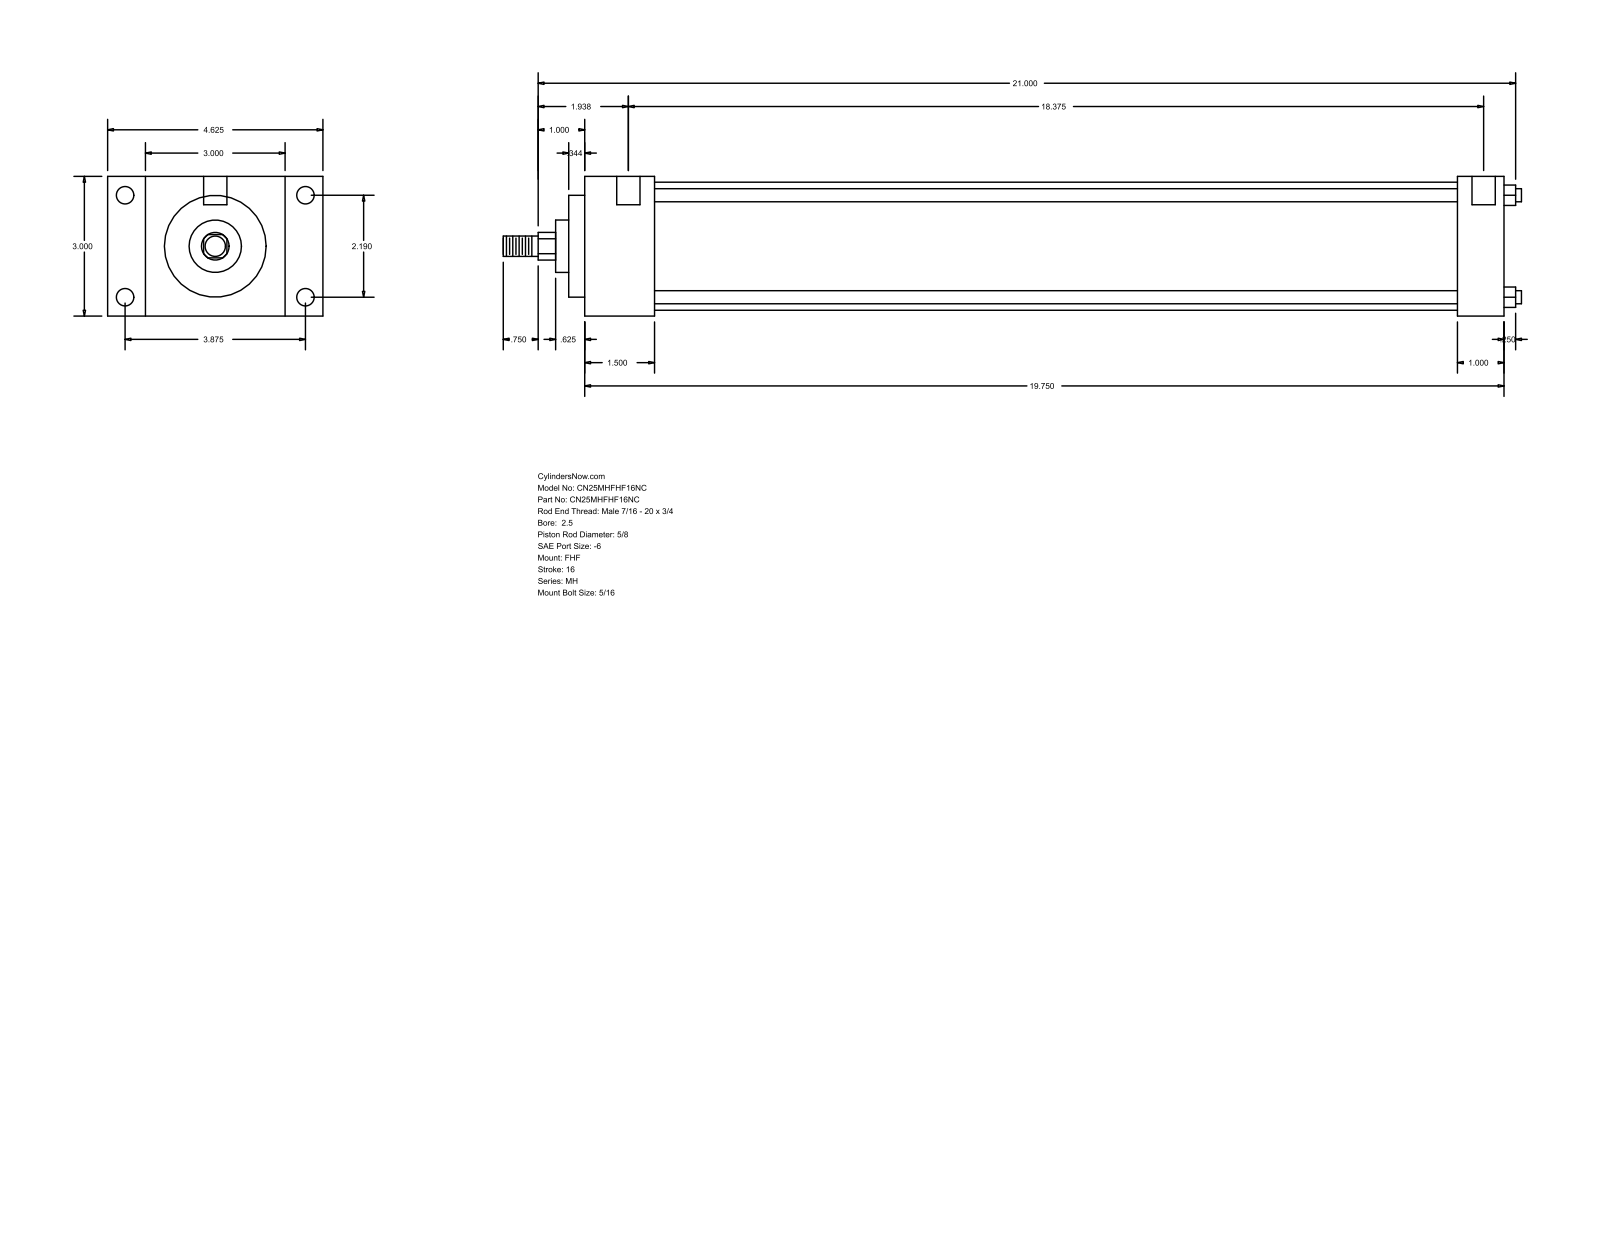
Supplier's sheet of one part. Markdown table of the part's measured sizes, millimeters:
| quantity | value |
| --- | --- |
| part name | MH_FHF__0250_0.625 |
| STEP written by | GSSL Pune (CONFIG_CONTROL_DESIGN) |
| units | millimeters |
| bodies | 0 solids, 90 faces (61 planar, 29 cylindrical, 0 other) |
| overall size | 555.62 × 117.47 × 76.2 |
| round holes (diameter × count) | 5.56 × 4, 9.53 × 4, 12.7 × 2 |
| round bosses / shafts (diameter × count) | 7.14 × 4, 69.85 × 1, 55.55 × 1, 28.57 × 1, 15.88 × 1, 11.11 × 1 |
| partial cylindrical surfaces (radius × count) | 7.54 × 1 |
| main face-to-face distances | 76.2, 501.65, 38.1, 463.55, 20.64, 96.84, 117.48, 25.4, 476.25, 438.15 |
| hole center spacings | 55.62, 98.42, 113.05, 474.66, 3.17, 4.76, 466.73, 469.9 |
